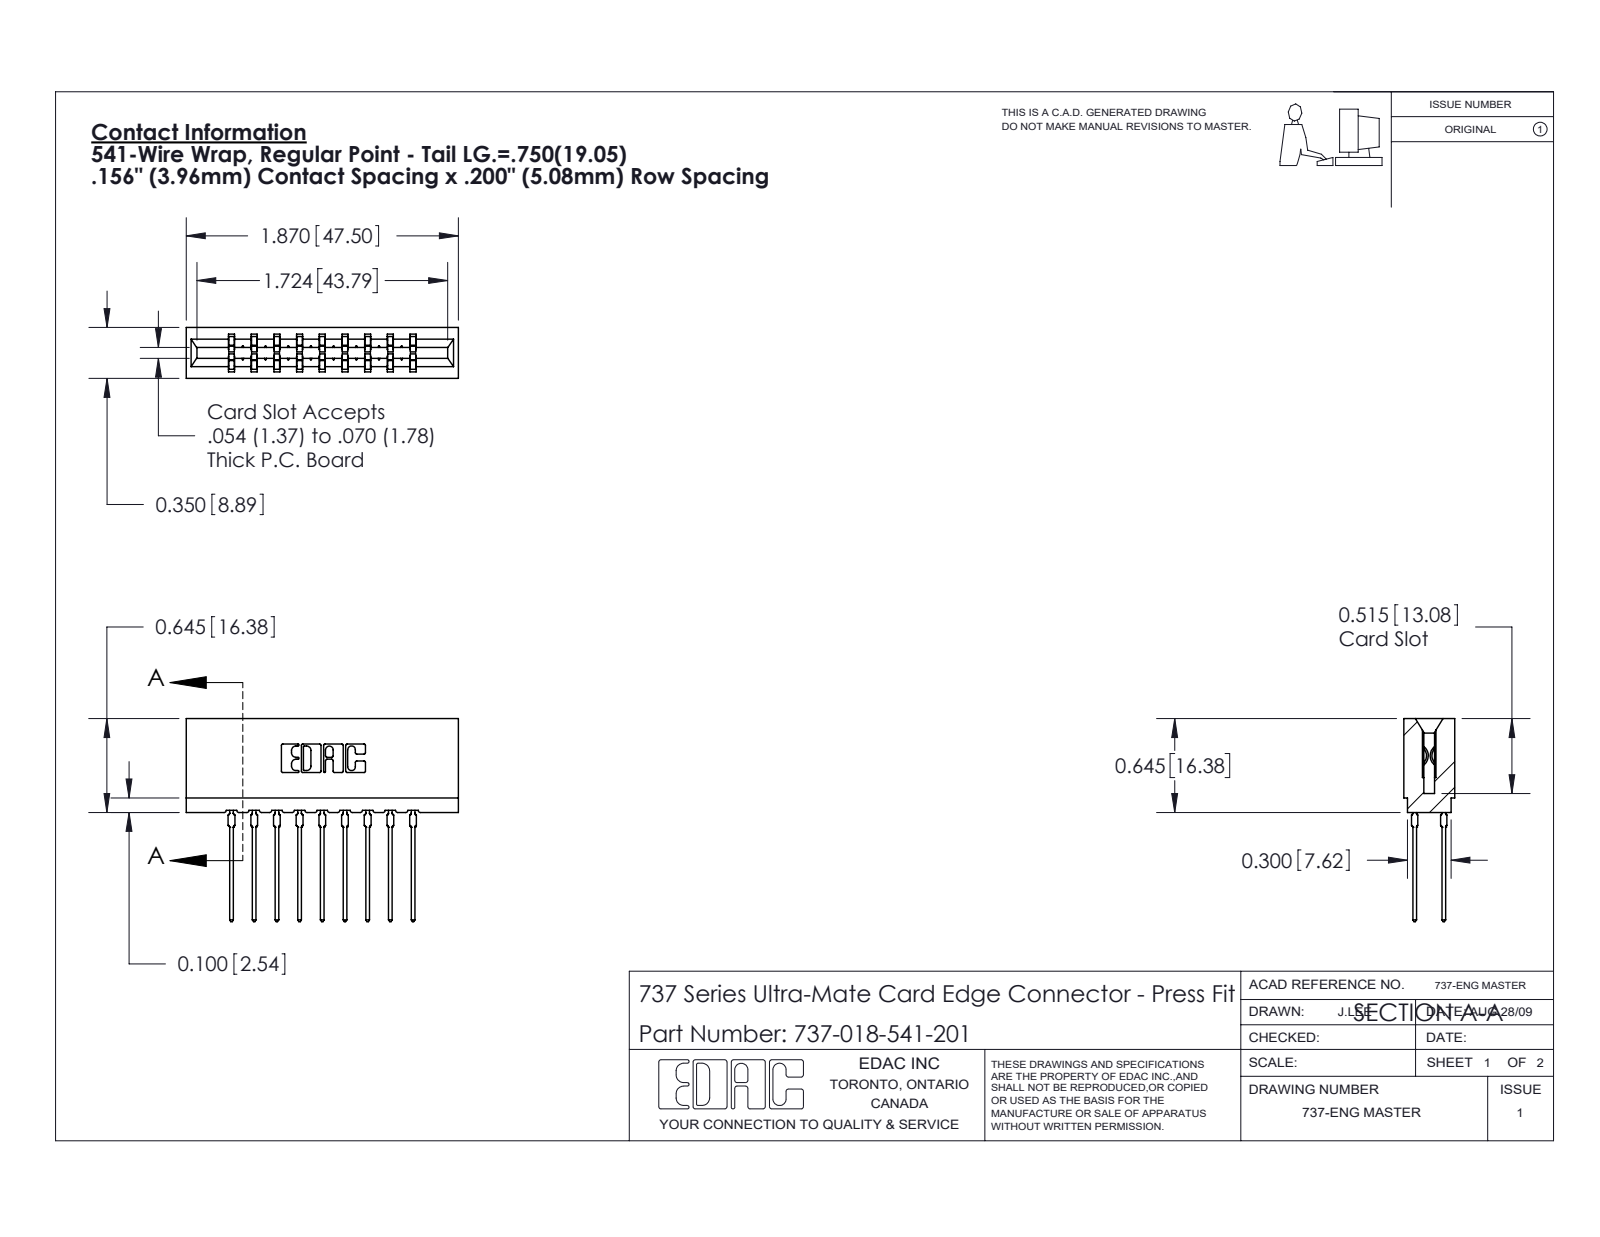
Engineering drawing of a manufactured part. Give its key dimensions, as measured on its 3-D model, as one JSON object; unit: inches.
{"part_name": "737-018-541-201; 737 Part_Insulator Option - 01; 745-292-001_541", "step_written_by": "SolidWorks 2020 (CONFIG_CONTROL_DESIGN)", "units": "inches", "bodies": {"solids": 19, "faces": 1714, "planar": 891, "cylindrical": 355, "other": 468}, "overall_size": [1.87, 1.396, 0.35], "volume_in3": 0.305, "surface_area_in2": 10.74, "partial_cylinders_radius": [[0.021, 36], [0.01, 22], [0.015, 18], [0.005, 8], [0.011, 8], [0.007, 6], [0.031, 6], [0.026, 3]], "face_to_face_distances": [0.156, 0.138, 0.212, 0.624, 0.35, 0.312, 0.468, 0.354, 0.78, 0.198]}
